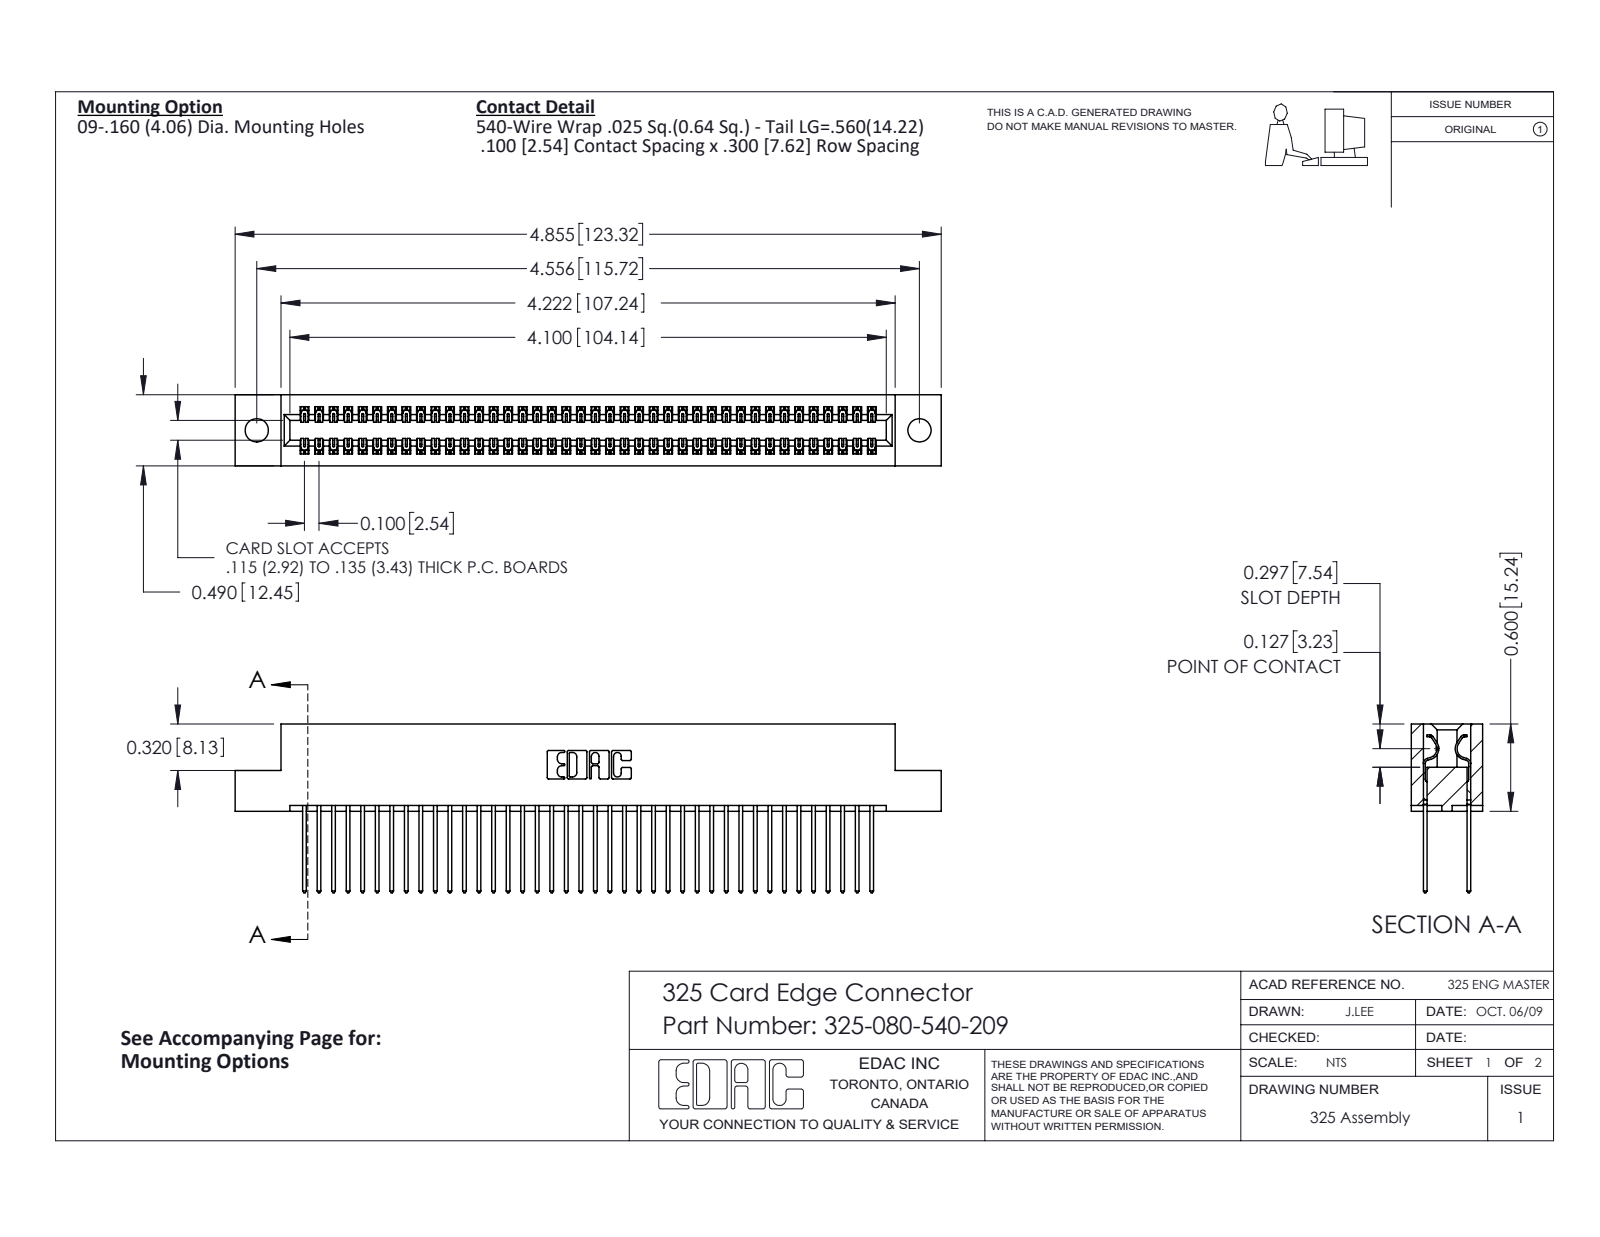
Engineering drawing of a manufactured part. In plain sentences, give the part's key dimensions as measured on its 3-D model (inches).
The part is named "325 Part_.160 TH; 325-080-540-209; 325-292-001_325-293-140". Its 3-D file was written by "SolidWorks 2016 (CONFIG_CONTROL_DESIGN)". It is 81 solids with 4274 faces: 2950 planar, 1324 cylindrical and 0 other. Overall it measures 4.855 by 1.16 by 0.49 inches. Its volume is 0.975 cubic inches and its surface area 32.01 square inches. Round holes: 2 of diameter 0.16. Partial cylindrical surfaces (rounded edges, fillets, slot ends): 120 of radius 0.006, 80 of radius 0.01, 22 of radius 0.01, 6 of radius 0.007, 6 of radius 0.031, 3 of radius 0.026, 2 of radius 0.014, 2 of radius 0.022. The main face-to-face distances are 0.083, 0.407, 0.3, 0.107, 0.383, 0.025, 0.49, 0.325, 0.275, 0.56. The hole center spacings are 4.556.
